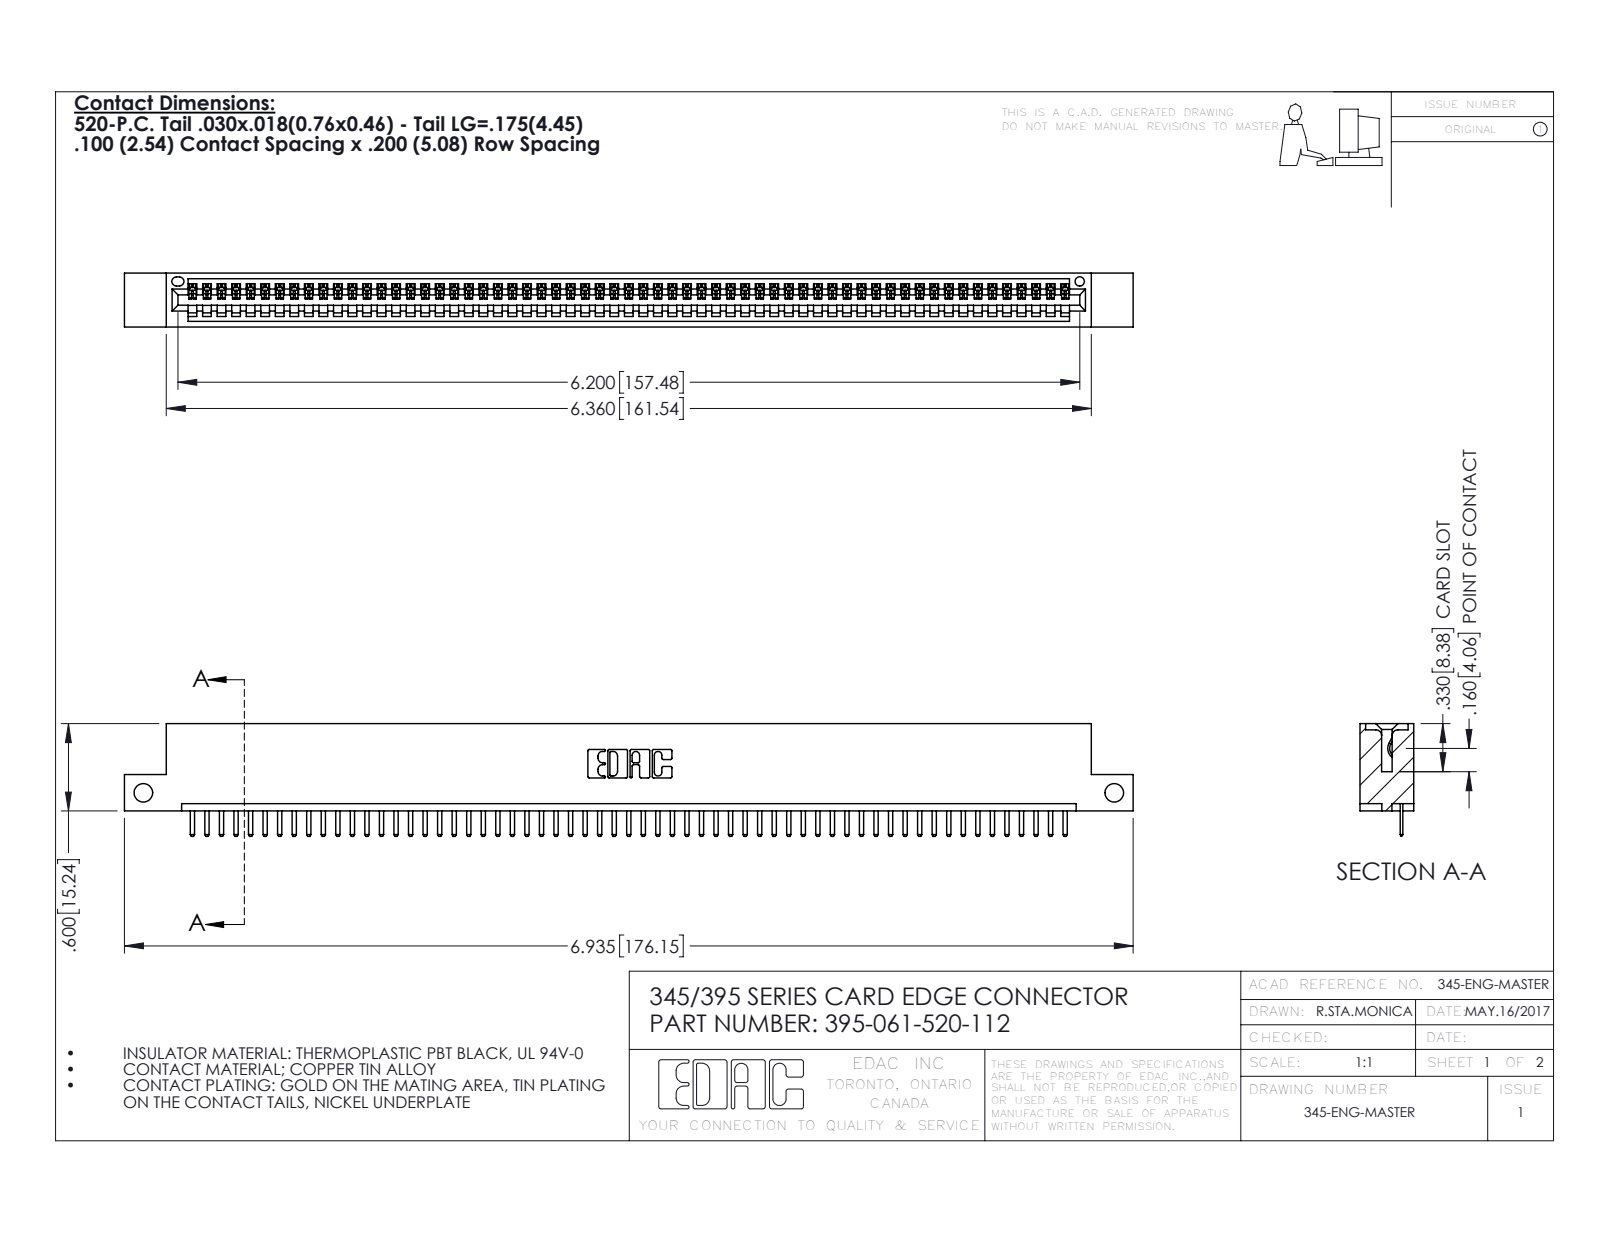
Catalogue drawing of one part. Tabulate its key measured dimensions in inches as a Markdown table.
| quantity | value |
| --- | --- |
| part name | 345-292-001_345-293-120; 395-061-520-112; 345 Part_Flush Mounting Lugs - Side Mount |
| STEP written by | SolidWorks 2016 (CONFIG_CONTROL_DESIGN) |
| units | inches |
| bodies | 62 solids, 3908 faces (2642 planar, 1266 cylindrical, 0 other) |
| overall size | 6.935 × 0.775 × 0.37 |
| volume | 1.014 in³ |
| surface area | 33.53 in² |
| round holes (diameter × count) | 0.128 × 2, 0.064 × 1 |
| partial cylindrical surfaces (radius × count) | 0.01 × 124, 0.006 × 122, 0.01 × 22, 0.007 × 6, 0.031 × 6, 0.026 × 3, 0.031 × 2, 0.04 × 2 |
| main face-to-face distances | 0.298, 0.072, 0.37, 0.2, 0.098, 0.272, 0.025, 0.225, 0.072, 0.149 |
| hole center spacings | 6.675 |
